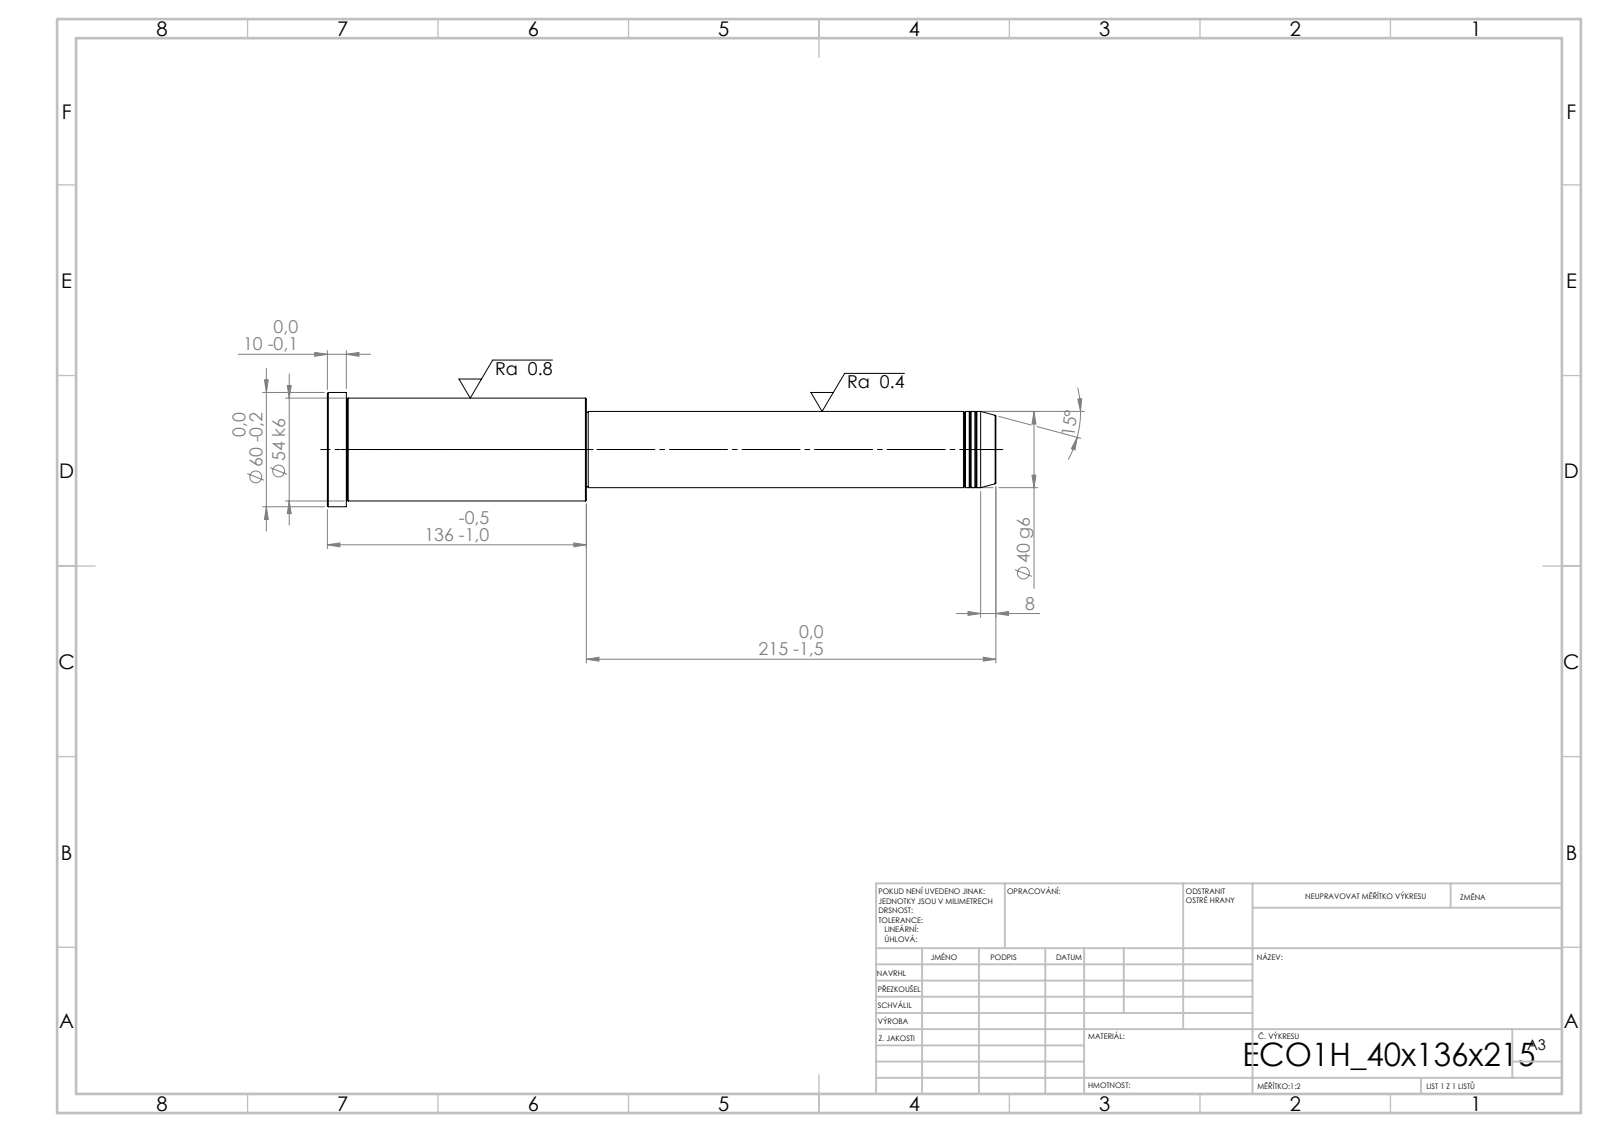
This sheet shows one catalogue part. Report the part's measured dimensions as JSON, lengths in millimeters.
{"step_written_by": "SolidWorks 2019 (CONFIG_CONTROL_DESIGN)", "units": "millimeters", "bodies": {"solids": 1, "faces": 43, "planar": 5, "cylindrical": 14, "other": 24}, "overall_size": [351, 60, 60], "volume_mm3": 585658, "surface_area_mm2": 55960, "round_bosses_or_shafts": [[60, 1], [54, 1], [40, 1], [39, 1]], "face_to_face_distances": [136, 215, 351, 341, 126, 10, 214, 1, 127, 137]}
